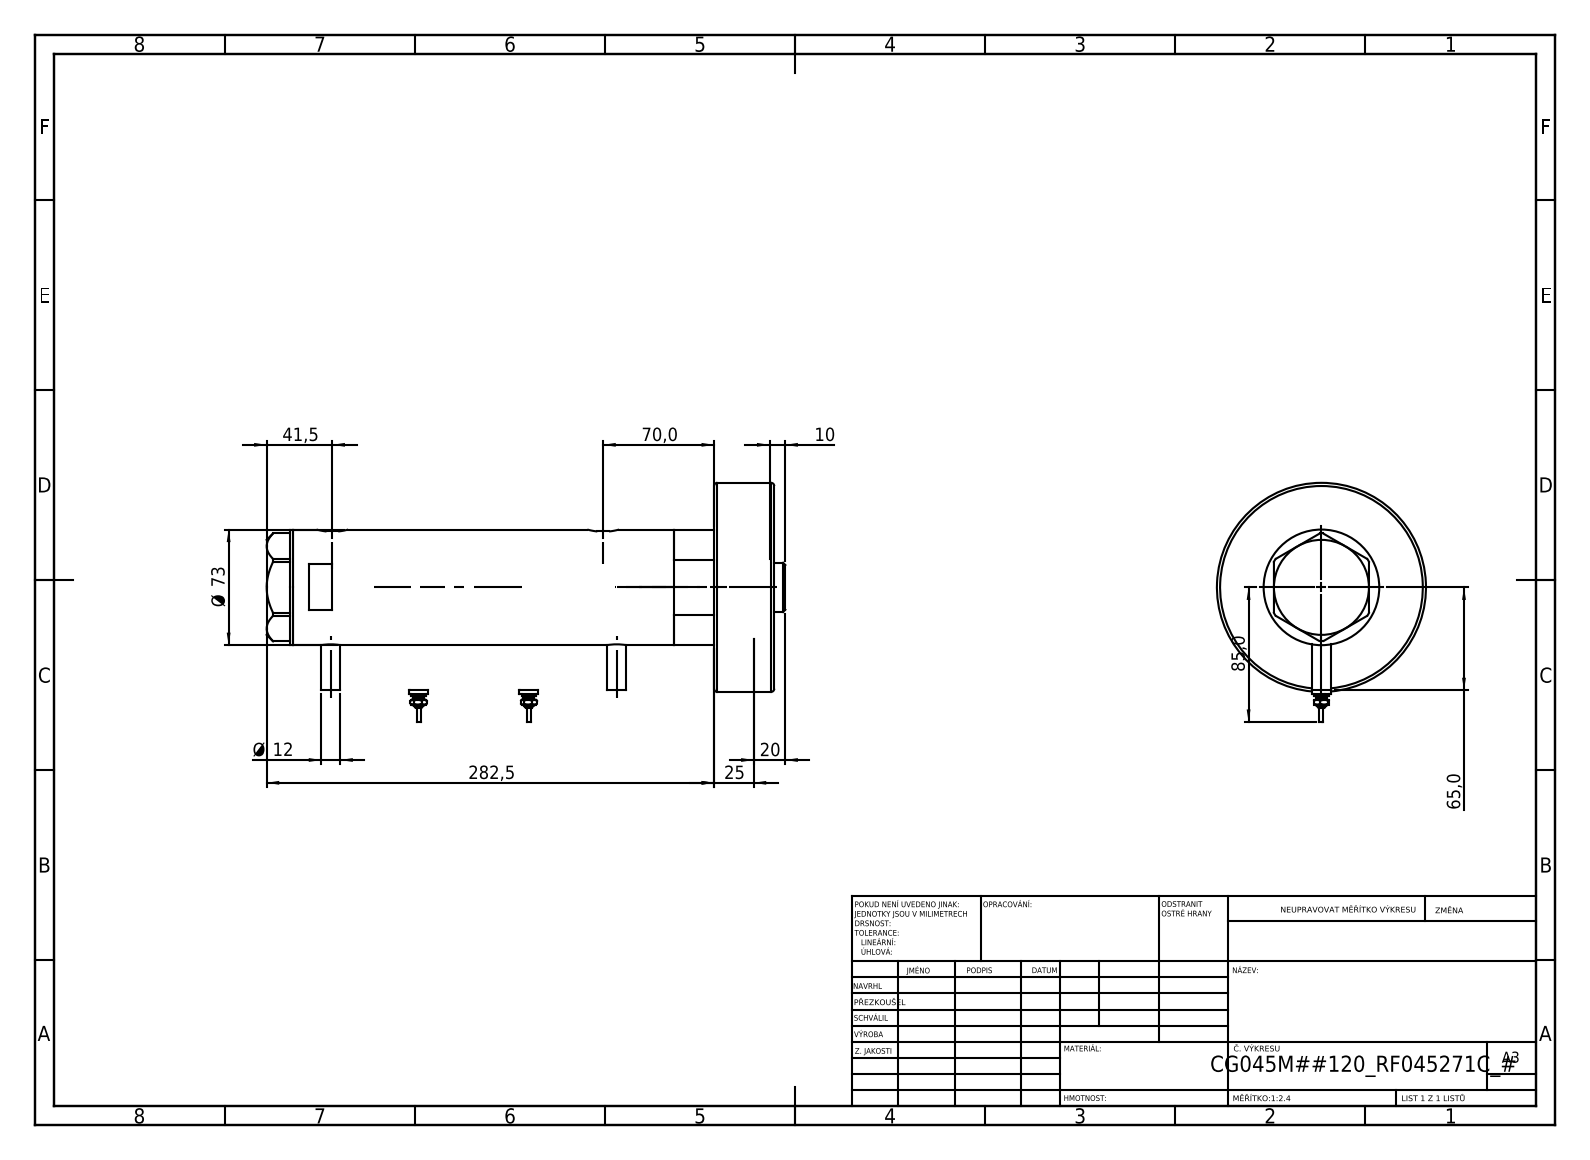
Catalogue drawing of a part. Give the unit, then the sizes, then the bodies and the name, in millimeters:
Units: millimetres
Overall size (bounding box): 327.5 × 151 × 132
Round holes (diameter × count): ⌀12.5 ×2, ⌀13.16 ×2, ⌀10.5 ×1, ⌀32 ×1, ⌀33.5 ×1, ⌀45 ×1, ⌀48 ×1, ⌀60 ×1, ⌀64 ×1
Round bosses / shafts (diameter × count): ⌀12 ×4, ⌀9 ×2, ⌀7 ×2, ⌀4.5 ×2, ⌀2.5 ×2, ⌀132 ×1, ⌀73 ×1, ⌀58 ×1
Partial cylindrical surfaces — rounded edges, fillets, slot ends (radius × count): R10 ×2
Main face-to-face distances: 38, 266, 304, 196, 70, 108, 26, 170, 240, 278
Hole centre spacings: 1, 8.5, 171, 172, 179.5, 180.5
Volume: 1 563 000 mm³ · Surface area: 231 197 mm²
Bodies: 7 solids, 222 faces (79 planar, 75 cylindrical, 68 other)
Part name (STEP PRODUCT): V270CG_BACK; V270CG_271C; V270CG_FRONT; V270CG_MIDDLE (+2 more)
STEP written by: SolidWorks 2019 (CONFIG_CONTROL_DESIGN)
